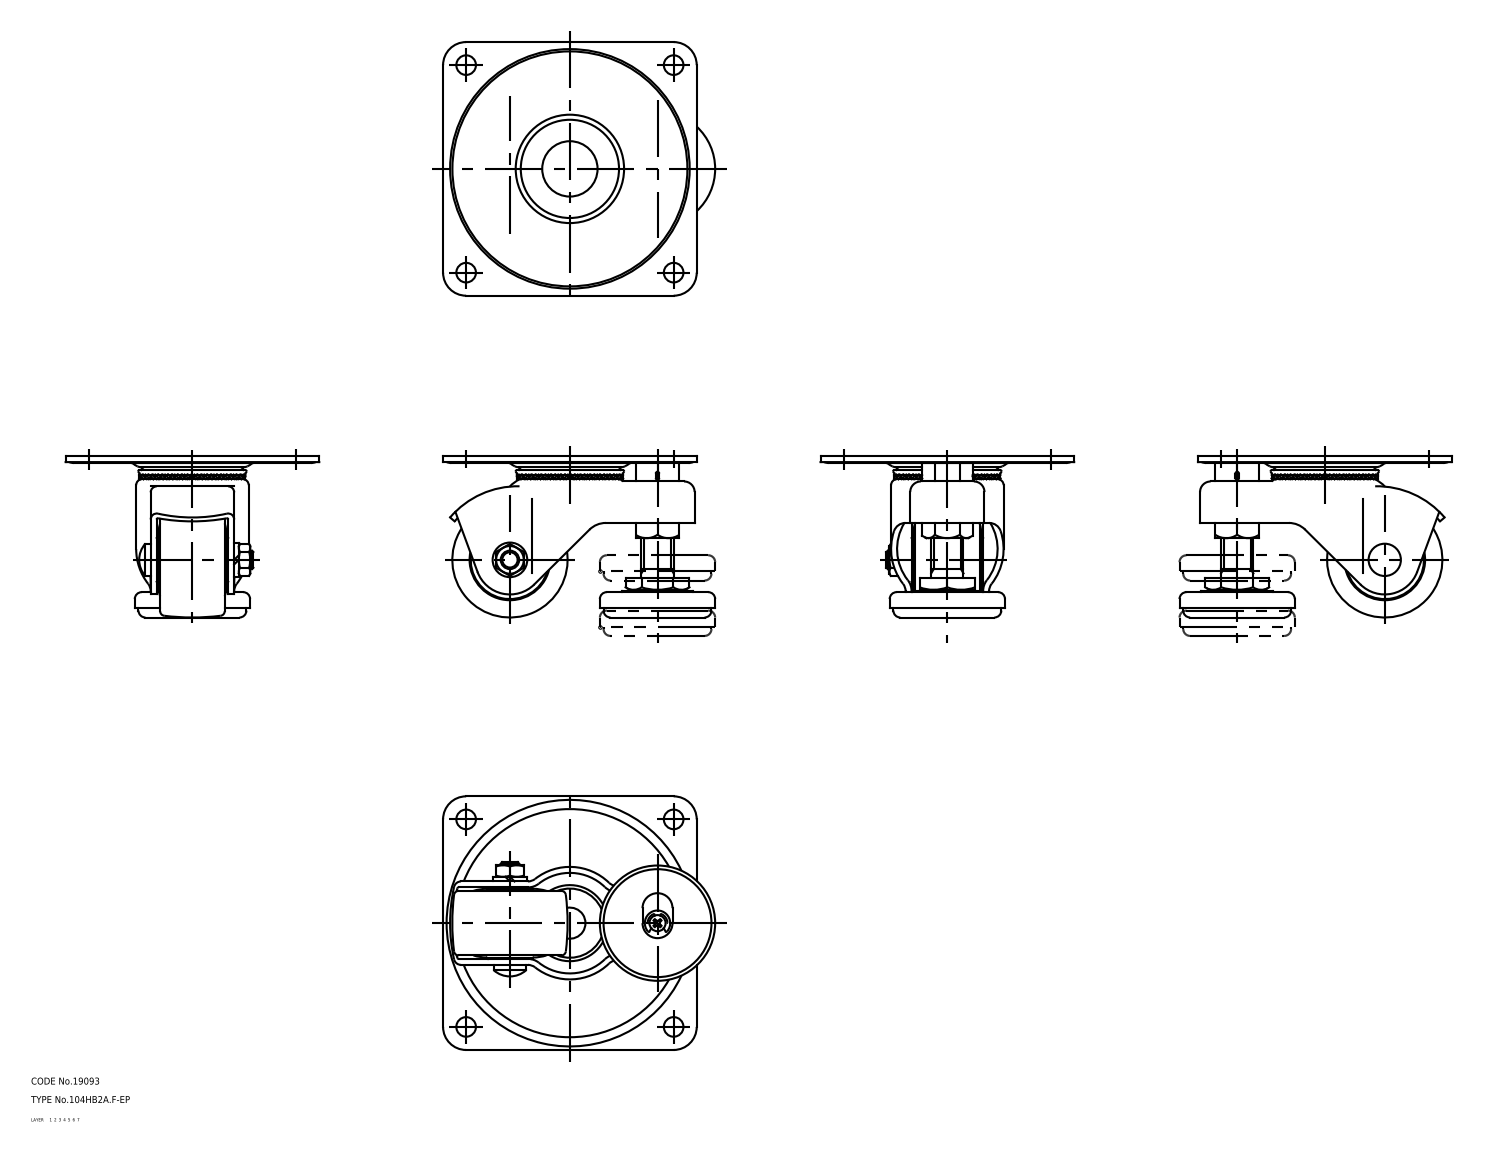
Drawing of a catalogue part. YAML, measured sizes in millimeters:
part_name: "67131370; 67131383; 67131396; 67131409 (+2 more)"
step_written_by: "CADfix (AUTOMOTIVE_DESIGN)"
units: millimeters
bodies: {solids: 6, faces: 351, planar: 0, cylindrical: 0, other: 351}
overall_size: [118, 110, 70]
volume: 160601
surface_area: 68976
